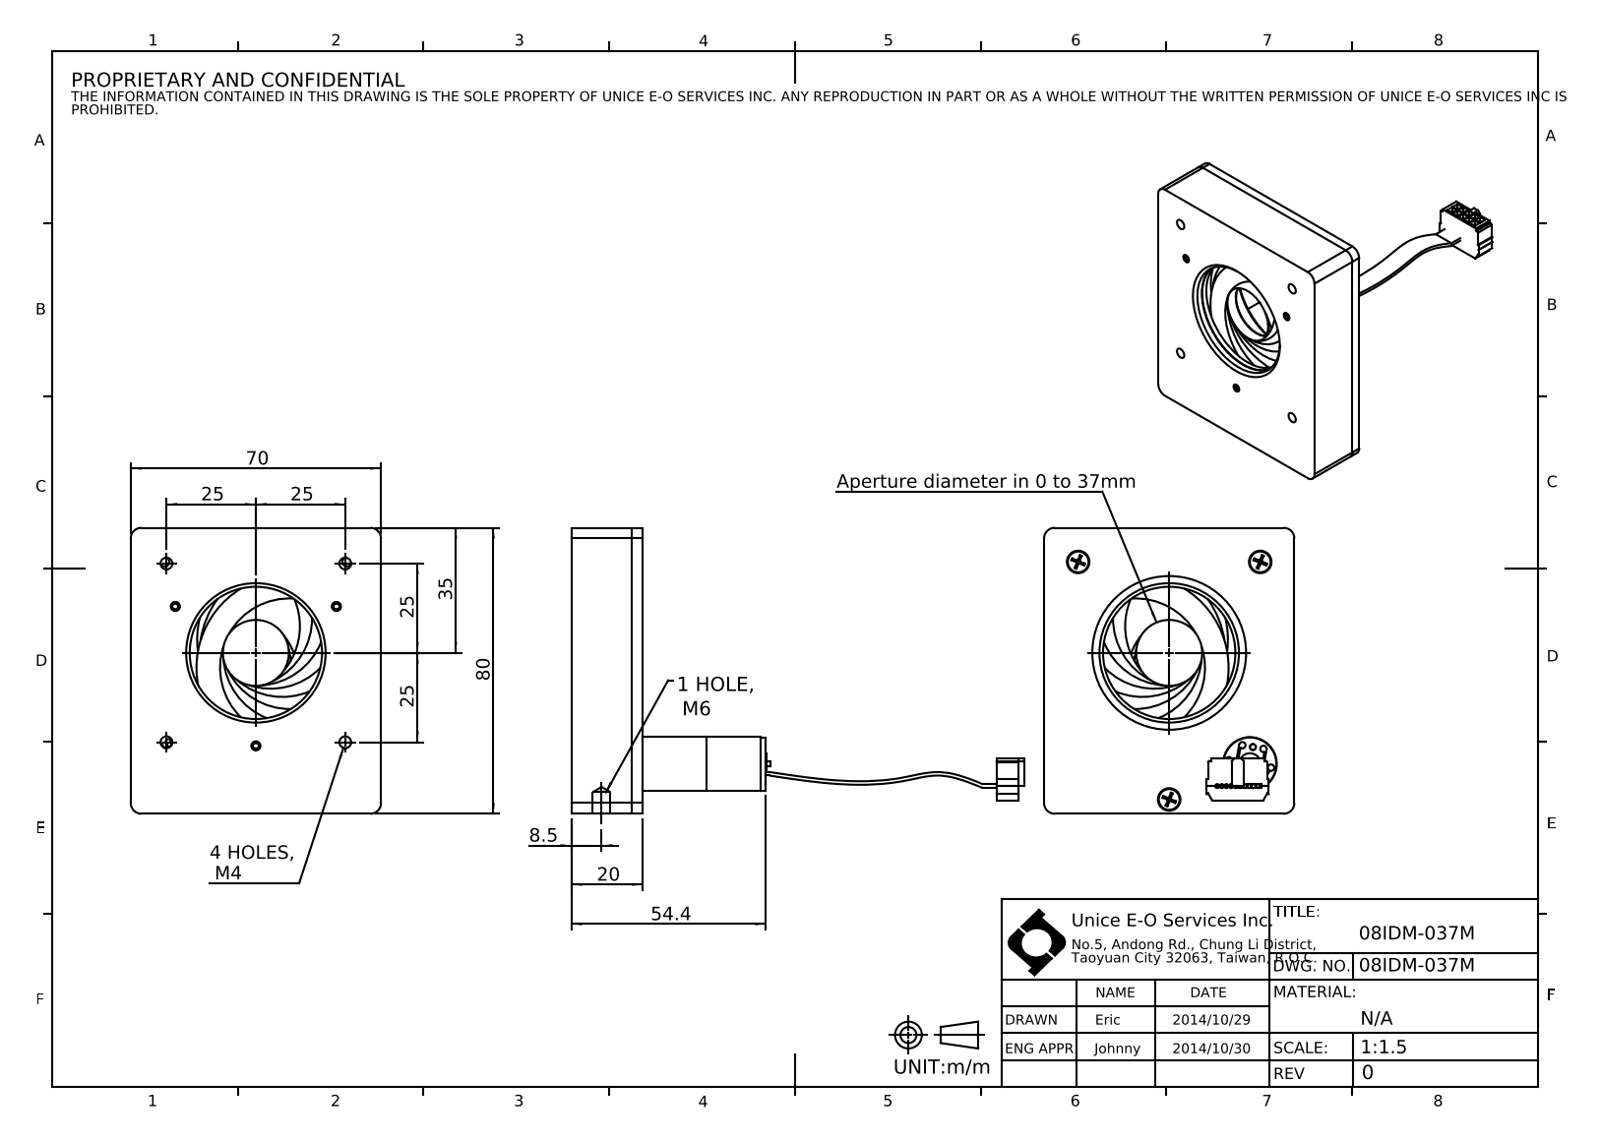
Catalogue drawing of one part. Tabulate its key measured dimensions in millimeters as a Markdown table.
| quantity | value |
| --- | --- |
| part name | 08IDM-037M |
| STEP written by | SolidWorks 2016 (CONFIG_CONTROL_DESIGN) |
| units | millimeters |
| bodies | 31 solids, 1550 faces (790 planar, 652 cylindrical, 108 other) |
| overall size | 126.6 × 80 × 70 |
| volume | 82 190 mm³ |
| surface area | 53 107 mm² |
| round holes (diameter × count) | 1.6 × 18, 2.5 × 8, 3.3 × 4, 3 × 3, 3.4 × 3, 1.1 × 2, 1.4 × 2, 1.48 × 2, 1.5 × 2, 2.4 × 2, 1.7 × 1, 3.1 × 1 |
| round bosses / shafts (diameter × count) | 1.8 × 8, 3 × 7, 5.8 × 3, 1.9 × 2, 1.38 × 2, 49.9 × 1, 15 × 1, 14.8 × 1 |
| partial cylindrical surfaces (radius × count) | 0.5 × 192, 0.48 × 10, 0.64 × 10, 2 × 6, 3 × 4, 0.51 × 2, 5 × 2, 5.4 × 1 |
| main face-to-face distances | 3, 17, 20, 1, 14, 4, 9.72, 3.92, 13, 70 |
| hole center spacings | 22, 16.84, 8.58, 24.45, 31.11, 40.65, 8.59, 35.36 |
